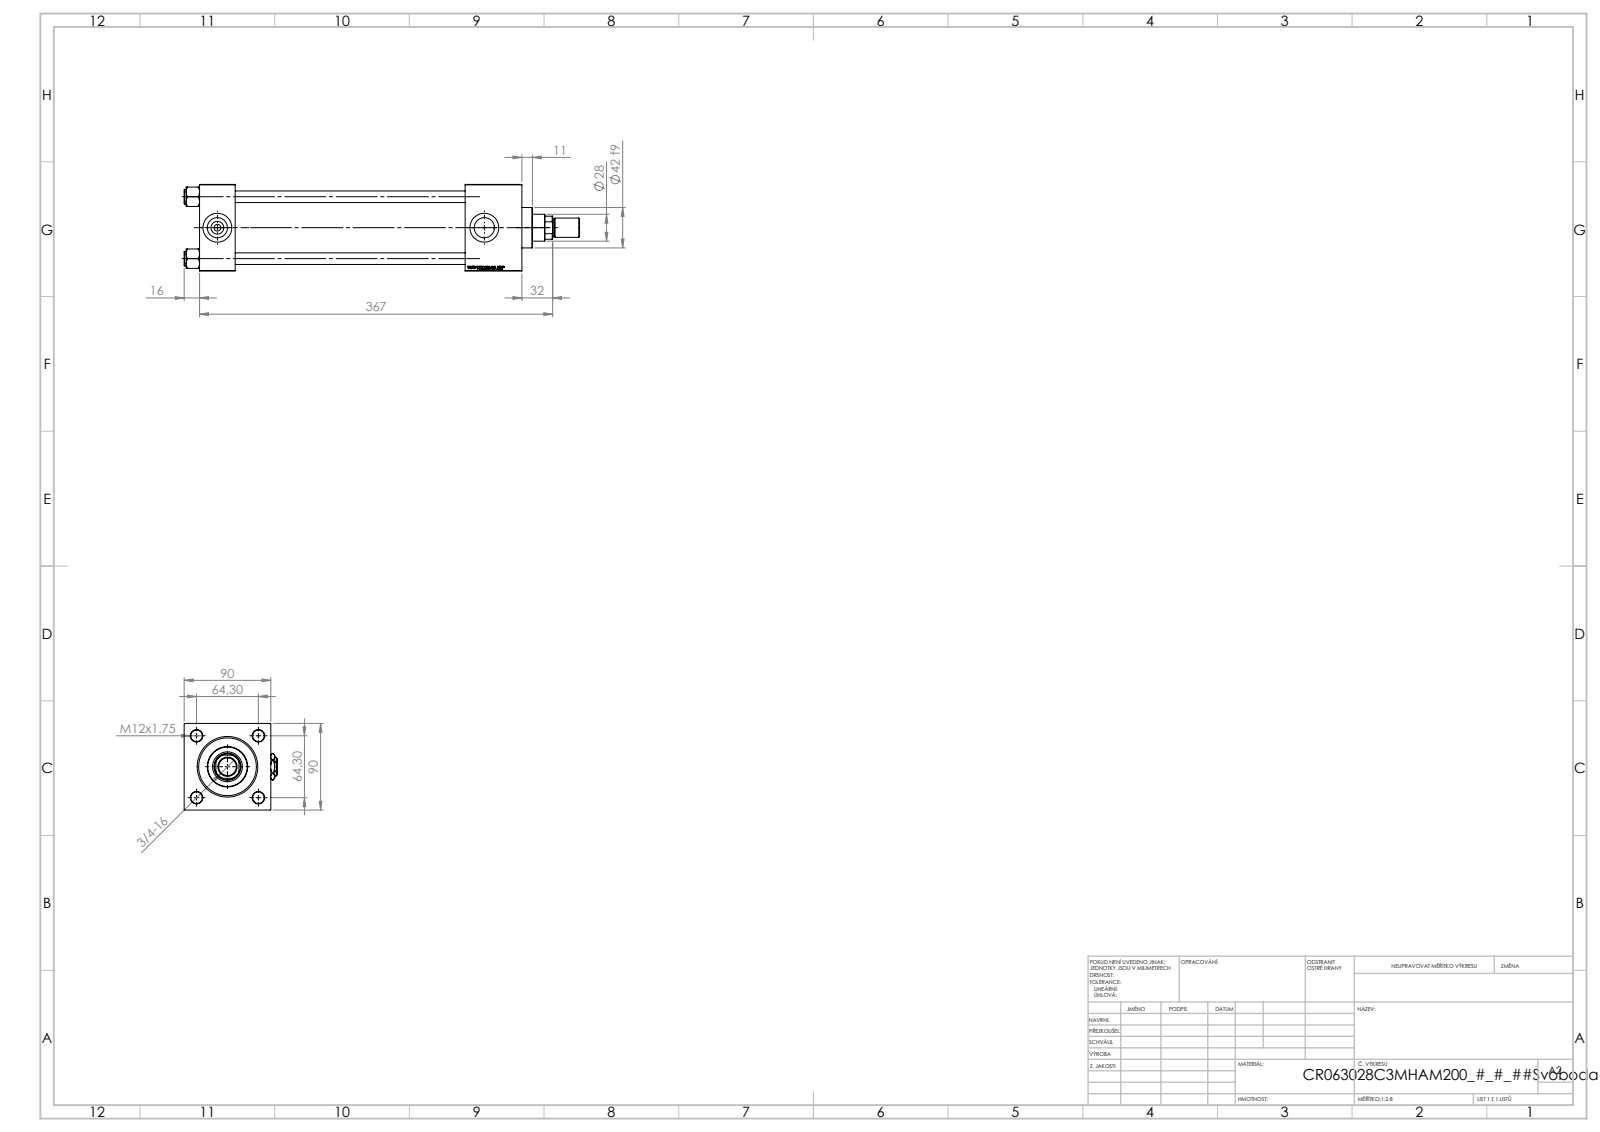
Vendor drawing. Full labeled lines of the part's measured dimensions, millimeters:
Part name (STEP PRODUCT): V215_VC_A; ROD_END_AH; V215CR_C_TYCINKA; Zatka_pro_OIL_PORT (+3 more)
STEP written by: SolidWorks 2019 (CONFIG_CONTROL_DESIGN)
Units: millimetres
Bodies: 14 solids, 1264 faces (578 planar, 102 cylindrical, 584 other)
Overall size (bounding box): 411 × 97 × 90
Volume: 1 253 000 mm³ · Surface area: 303 970 mm²
Round holes (diameter × count): ⌀12 ×4, ⌀7 ×2, ⌀20.96 ×2, ⌀30 ×2, ⌀18.5 ×1, ⌀28 ×1, ⌀31 ×1, ⌀50 ×1, ⌀60 ×1, ⌀63 ×1
Round bosses / shafts (diameter × count): ⌀15 ×4, ⌀69 ×1, ⌀42 ×1, ⌀20 ×1, ⌀18 ×1
Partial cylindrical surfaces — rounded edges, fillets, slot ends (radius × count): R13.5 ×1
Main face-to-face distances: 90, 37, 298, 335, 59, 276, 239, 306.3, 269.3, 30.3
Hole centre spacings: 45.47, 64.3, 90.93, 277.5
